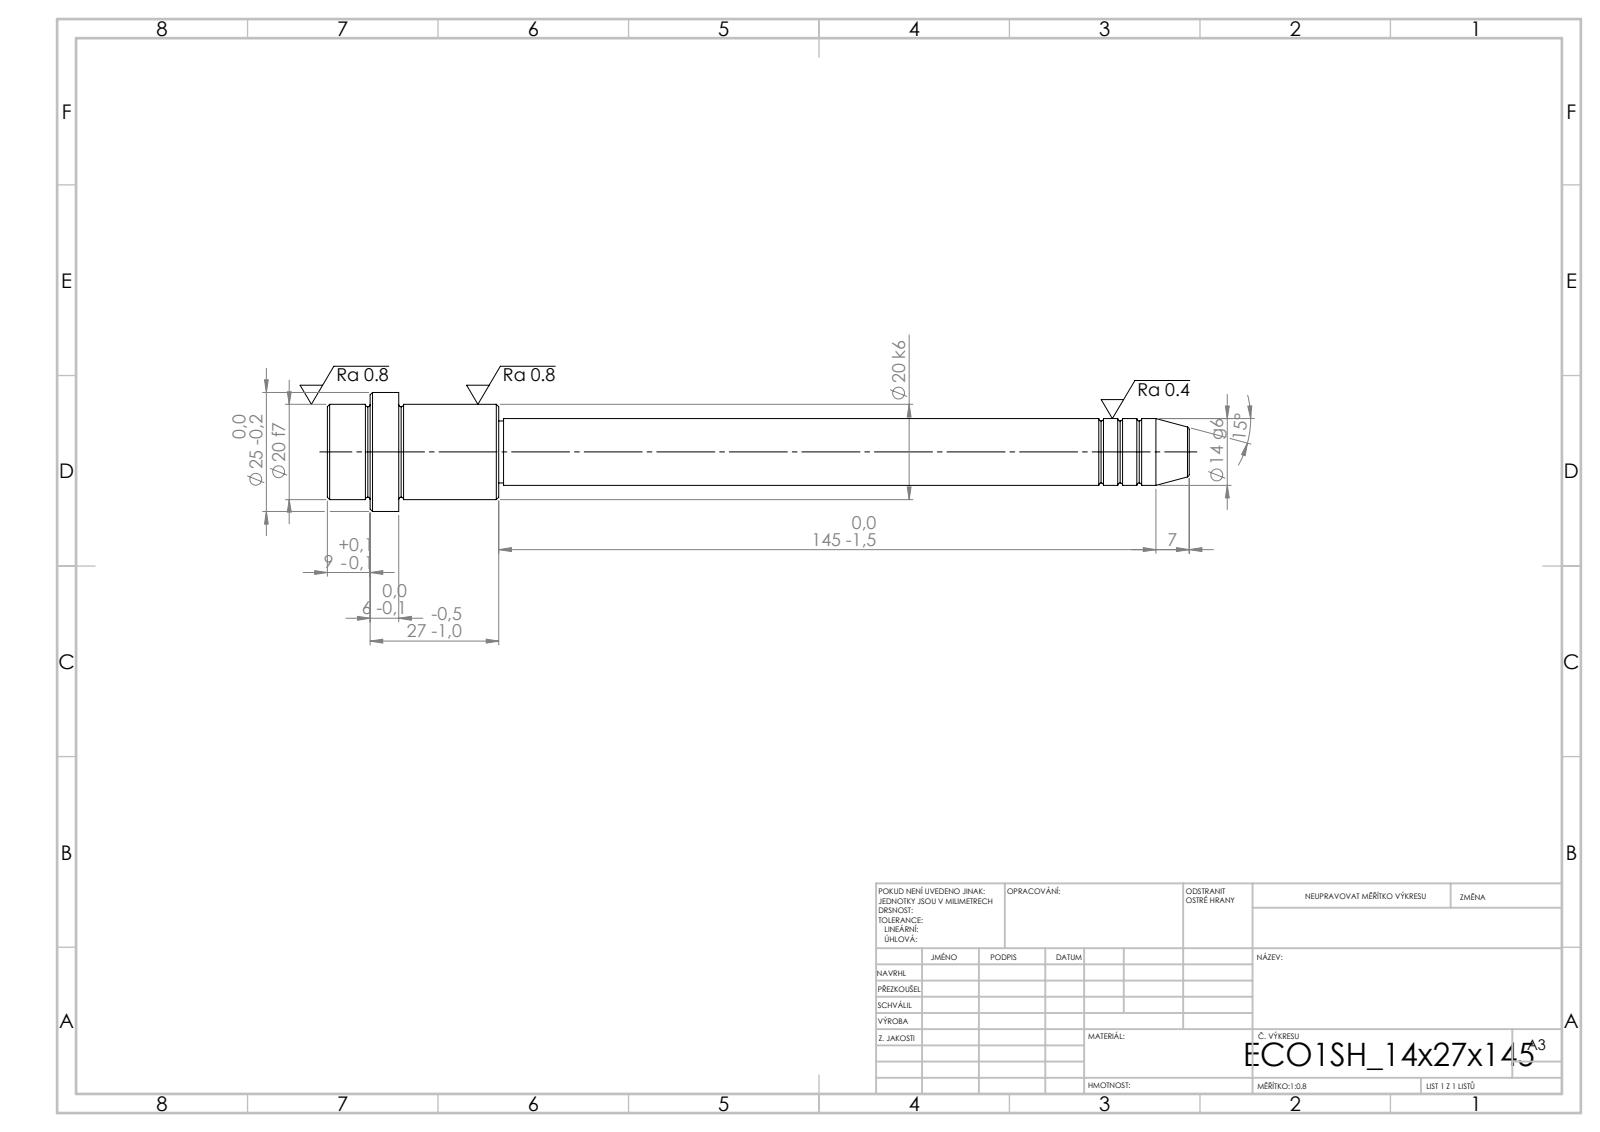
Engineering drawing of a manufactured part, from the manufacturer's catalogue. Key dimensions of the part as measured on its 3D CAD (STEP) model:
STEP written by: SolidWorks 2019 (CONFIG_CONTROL_DESIGN)
Units: millimetres
Bodies: 1 solid, 52 faces (6 planar, 16 cylindrical, 30 other)
Overall size (bounding box): 181 × 25 × 25
Volume: 34 282 mm³ · Surface area: 9 718 mm²
Round bosses / shafts (diameter × count): ⌀25 ×1, ⌀20 ×1, ⌀14 ×1, ⌀13 ×1
Main face-to-face distances: 15, 21, 36, 27, 6, 9, 145, 166, 172, 181
